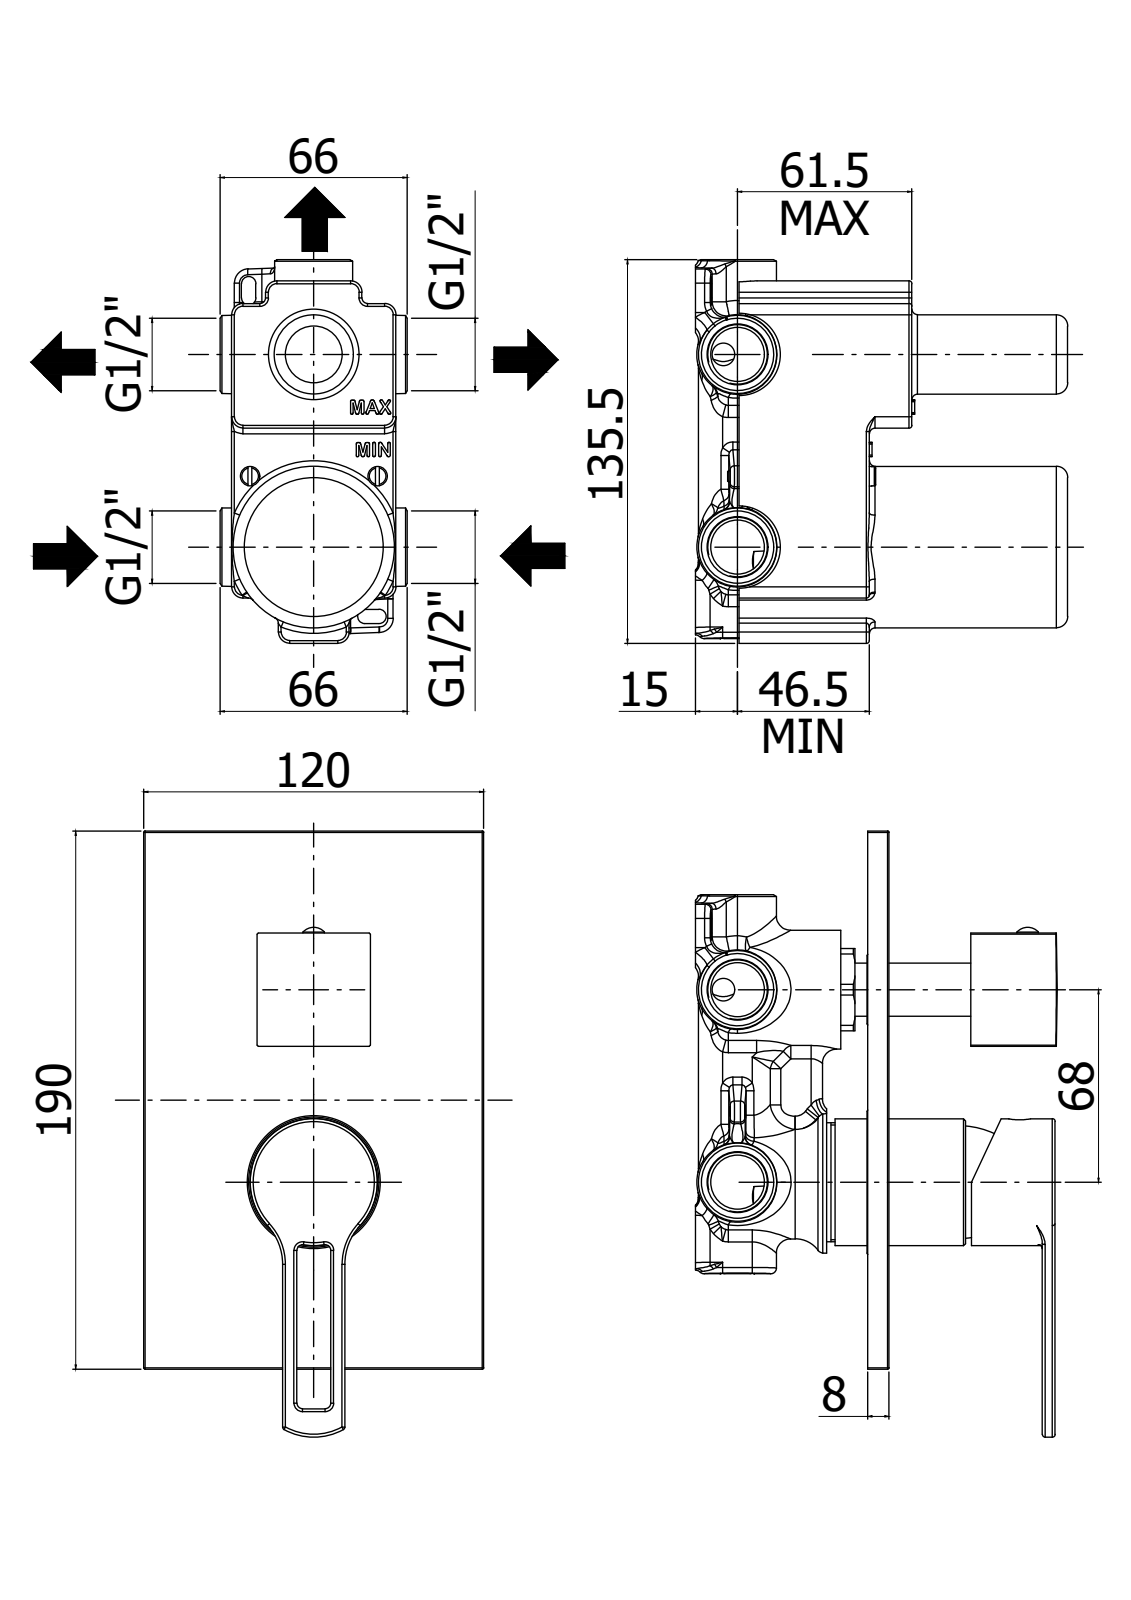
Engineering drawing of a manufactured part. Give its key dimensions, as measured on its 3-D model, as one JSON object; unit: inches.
{"part_name": "RIN018CR", "step_written_by": "CREO PARAMETRIC BY PTC INC, 2020044 (CONFIG_CONTROL_DESIGN)", "units": "inches", "bodies": {"solids": 4, "faces": 1162, "planar": 609, "cylindrical": 299, "other": 254}, "overall_size": [8.425, 4.724, 2.215], "volume_in3": 12.02, "surface_area_in2": 164, "round_holes": [[0.118, 2], [0.157, 2], [1.417, 2], [0.126, 1], [0.13, 1], [0.165, 1], [0.177, 1], [0.197, 1], [0.307, 1], [0.433, 1], [0.583, 1], [0.756, 1]], "round_bosses_or_shafts": [[0.299, 2], [0.217, 2], [2.008, 1], [1.929, 1], [1.764, 1], [1.575, 1], [1.378, 1], [0.984, 1]], "partial_cylinders_radius": [[0.02, 22], [0.039, 22], [0.006, 11], [0.012, 4], [0.079, 4], [0.787, 2], [0.276, 1], [0.366, 1]], "face_to_face_distances": [0.315, 0.098, 0.217, 0.886, 2.15, 1.933, 1.835, 3.839, 0.02, 4.724], "hole_center_spacings": [0.15, 0.394, 0.433, 0.583, 2.677, 3.071]}
